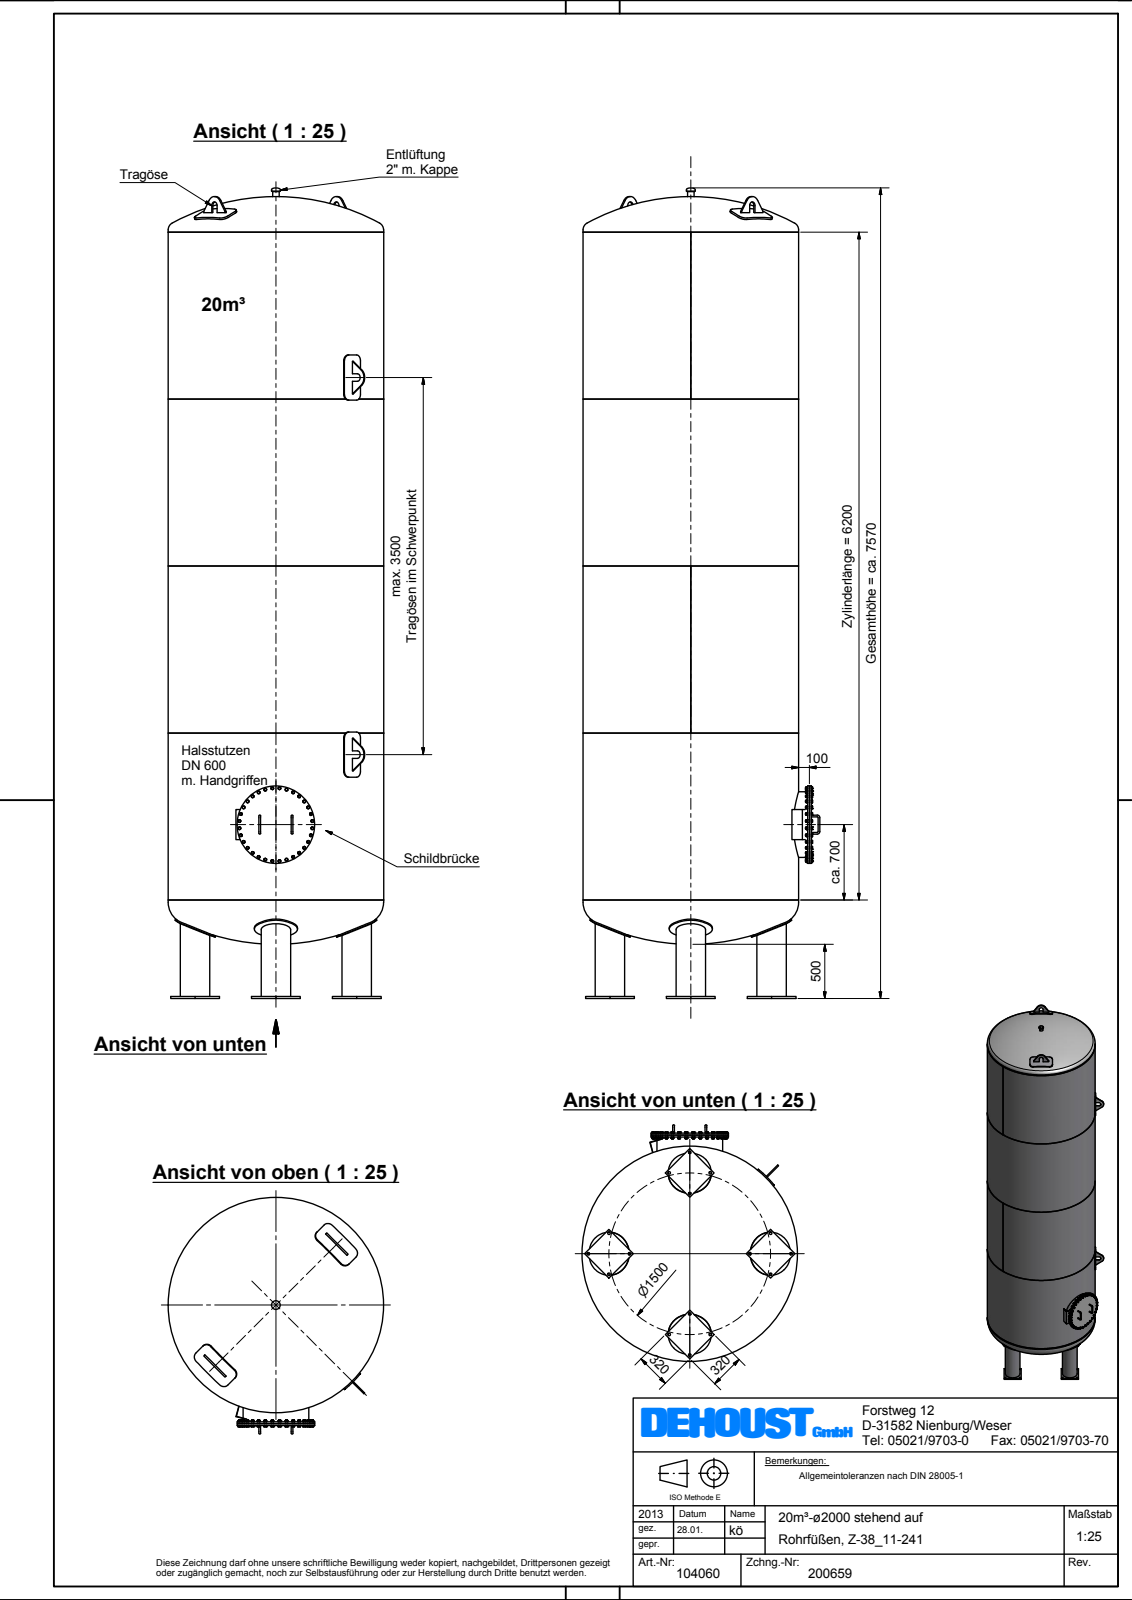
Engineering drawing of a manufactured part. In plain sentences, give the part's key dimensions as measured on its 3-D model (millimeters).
The part is named "Beh\\S\\dlter_Z-38_11-241_2000_020_KV". Its 3-D file was written by "Autodesk Inventor 2012 (AUTOMOTIVE_DESIGN)". It is 7 solids with 1116 faces: 632 planar, 162 cylindrical and 322 other. Overall it measures 7525.43 by 2197 by 2000 millimeters. Its volume is 1 175 000 000 cubic millimeters and its surface area 100 600 000 square millimeters. Round holes: 4 of diameter 257, 1 of diameter 598, 1 of diameter 1988. Round bosses or shafts: 38 of diameter 16, 32 of diameter 22.5, 4 of diameter 400, 4 of diameter 273, 1 of diameter 2000, 1 of diameter 720, 1 of diameter 660, 1 of diameter 610. Partial cylindrical surfaces (rounded edges, fillets, slot ends): 16 of radius 56, 4 of radius 35, 4 of radius 85, 1 of radius 1010. The main face-to-face distances are 914.59, 20, 35, 894.59, 16, 19, 10, 3, 2.95, 176.98. The hole center spacings are 750, 1060.66, 1500.
